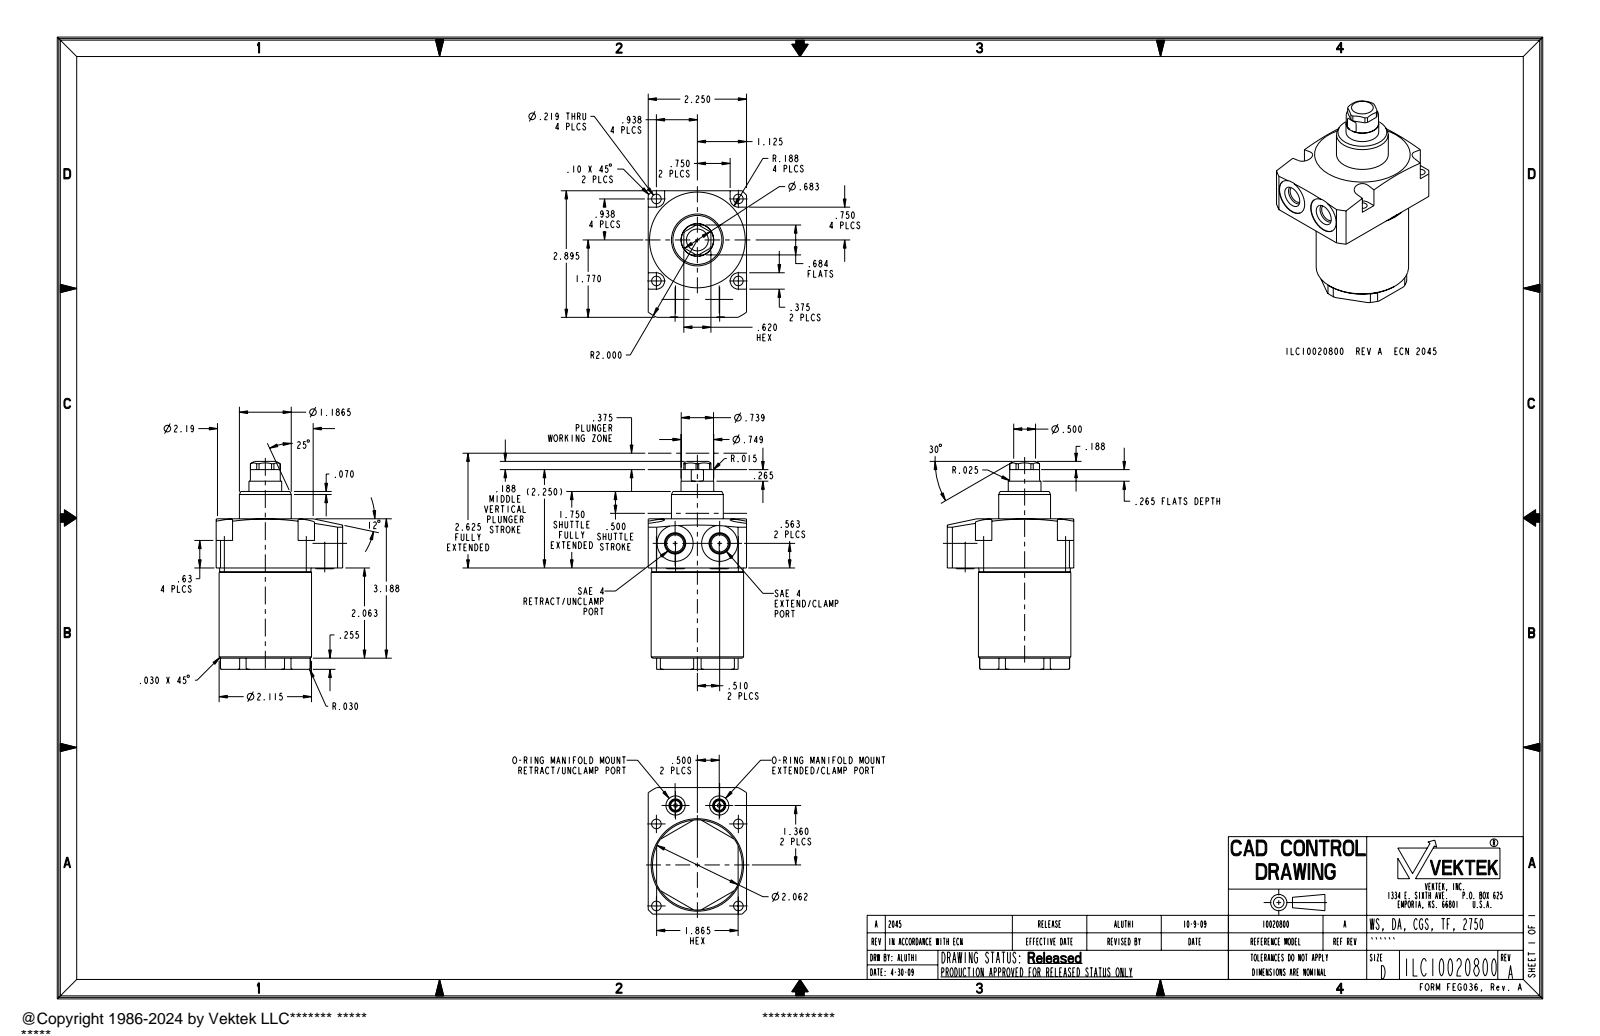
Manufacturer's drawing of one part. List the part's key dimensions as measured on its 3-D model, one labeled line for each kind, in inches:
Part name (STEP PRODUCT): ILC10020800
STEP written by: PRO/ENGINEER BY PARAMETRIC TECHNOLOGY CORPORATION, 2007460 (AUTOMOTIVE_DESIGN_CC2)
Units: inches
Bodies: 1 solid, 194 faces (82 planar, 76 cylindrical, 36 other)
Overall size (bounding box): 4.756 × 2.895 × 2.25
Volume: 15.58 in³ · Surface area: 47.92 in²
Round holes (diameter × count): ⌀0.219 ×4, ⌀0.098 ×2, ⌀0.266 ×2, ⌀0.392 ×2, ⌀0.439 ×2, ⌀0.825 ×2
Round bosses / shafts (diameter × count): ⌀0.437 ×2, ⌀0.255 ×2, ⌀0.224 ×2, ⌀0.118 ×2, ⌀2.115 ×1, ⌀2.09 ×1, ⌀1.187 ×1, ⌀0.749 ×1
Partial cylindrical surfaces — rounded edges, fillets, slot ends (radius × count): R0.025 ×2, R0.187 ×2, R0.188 ×2, R0.341 ×1, R1.031 ×1, R2 ×1
Main face-to-face distances: 3.443, 2.25, 2.318, 1.125, 2.895, 2.885, 4.068, 1.75, 0.625, 0.192
Hole centre spacings: 1.876, 0.608, 1.499, 2.339, 2.654, 2.711, 1, 1.02
